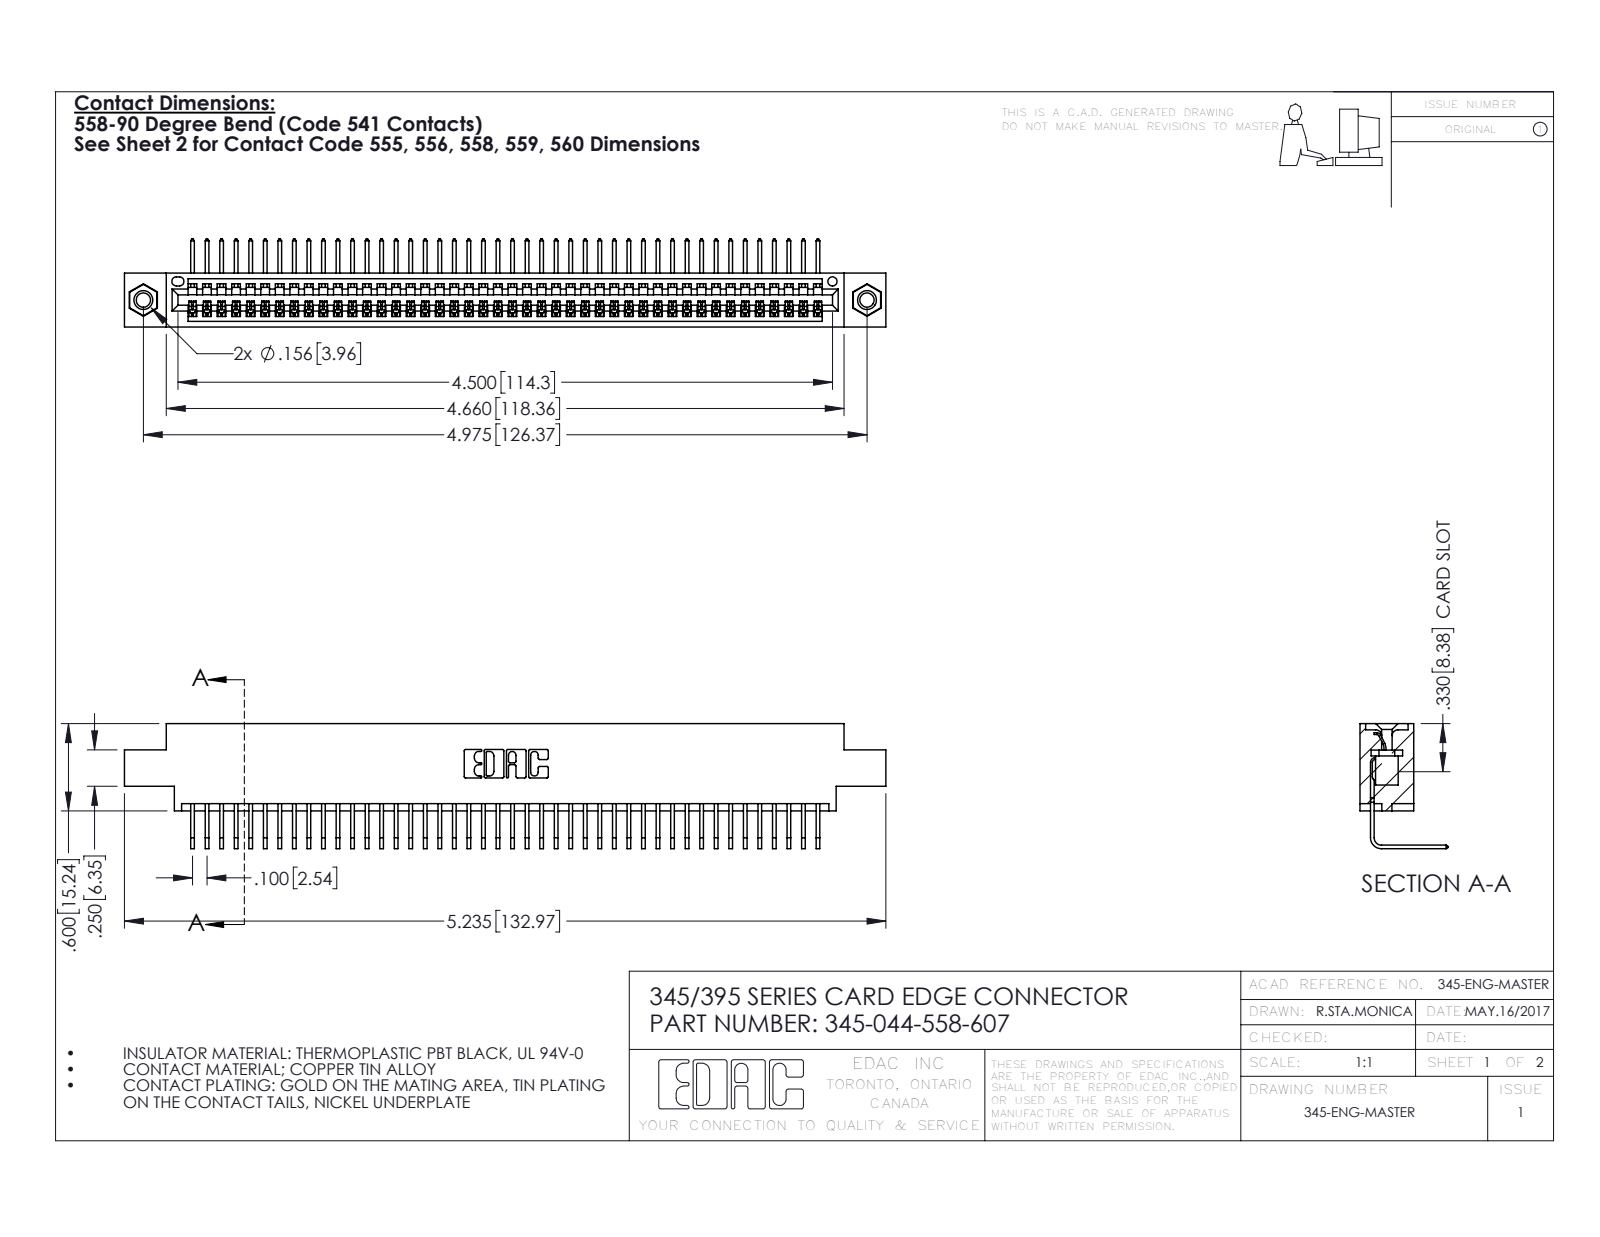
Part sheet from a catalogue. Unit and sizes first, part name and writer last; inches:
Units: inches
Overall size (bounding box): 5.235 × 0.859 × 0.605
Round holes (diameter × count): ⌀0.098 ×2, ⌀0.125 ×2, ⌀0.156 ×2, ⌀0.064 ×1
Round bosses / shafts (diameter × count): ⌀0.155 ×2
Partial cylindrical surfaces — rounded edges, fillets, slot ends (radius × count): R0.006 ×88, R0.01 ×22, R0.007 ×6, R0.031 ×6, R0.026 ×3, R0.031 ×2, R0.04 ×2, R0.014 ×1
Main face-to-face distances: 0.072, 0.298, 0.37, 0.2, 0.098, 0.272, 0.025, 0.225, 0.175, 0.149
Hole centre spacings: 0.27, 4.739, 4.975
Volume: 0.773 in³ · Surface area: 27.71 in²
Bodies: 47 solids, 2830 faces (1964 planar, 850 cylindrical, 16 other)
Part name (STEP PRODUCT): 345-250-001_345-250-005-103; 345 Part_0.170 Offset - 0.156 Dia-TI; 345-044-558-607; 345-292-001_558 Tail - 2
STEP written by: SolidWorks 2016 (CONFIG_CONTROL_DESIGN)
